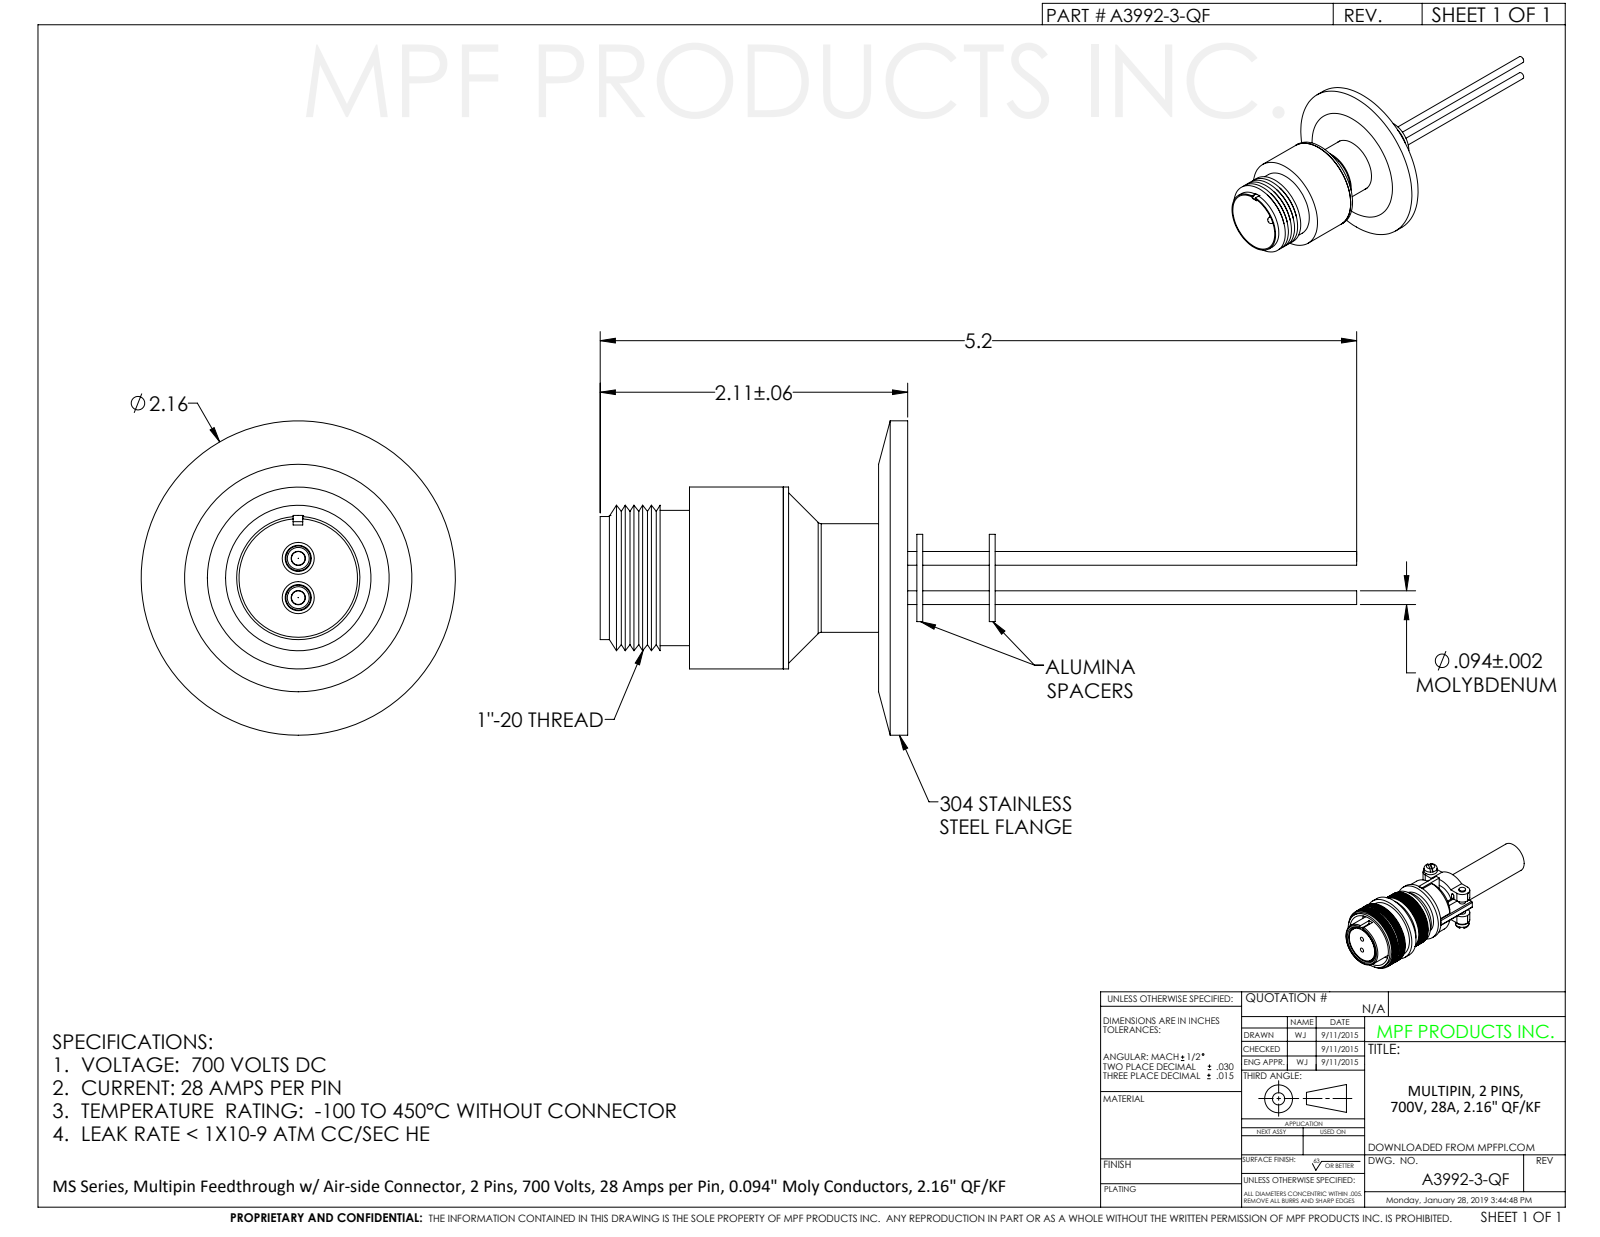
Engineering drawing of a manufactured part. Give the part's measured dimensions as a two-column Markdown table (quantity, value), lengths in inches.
| quantity | value |
| --- | --- |
| part name | A3992-3-QF |
| STEP written by | SolidWorks 2012 (CONFIG_CONTROL_DESIGN) |
| units | inches |
| bodies | 1 solid, 225 faces (37 planar, 78 cylindrical, 110 other) |
| overall size | 5.204 × 2.161 × 2.161 |
| volume | 1.153 in³ |
| surface area | 30.03 in² |
| round holes (diameter × count) | 0.085 × 2, 0.085 × 2, 0.171 × 2, 0.63 × 1, 0.675 × 1, 0.815 × 1, 0.935 × 1, 0.98 × 1, 1.17 × 1, 1.63 × 1 |
| round bosses / shafts (diameter × count) | 0.191 × 2, 0.182 × 2, 0.094 × 2, 2.161 × 1, 1.25 × 1, 1.07 × 1, 0.965 × 1, 0.928 × 1 |
| main face-to-face distances | 0.105, 0.2, 0.095, 1.353, 1.248, 1.153, 1.193, 1.088, 0.993, 0.16 |
| hole center spacings | 0.185, 0.262, 0.296, 0.131, 0.131, 0.135, 0.37, 0.27 |
